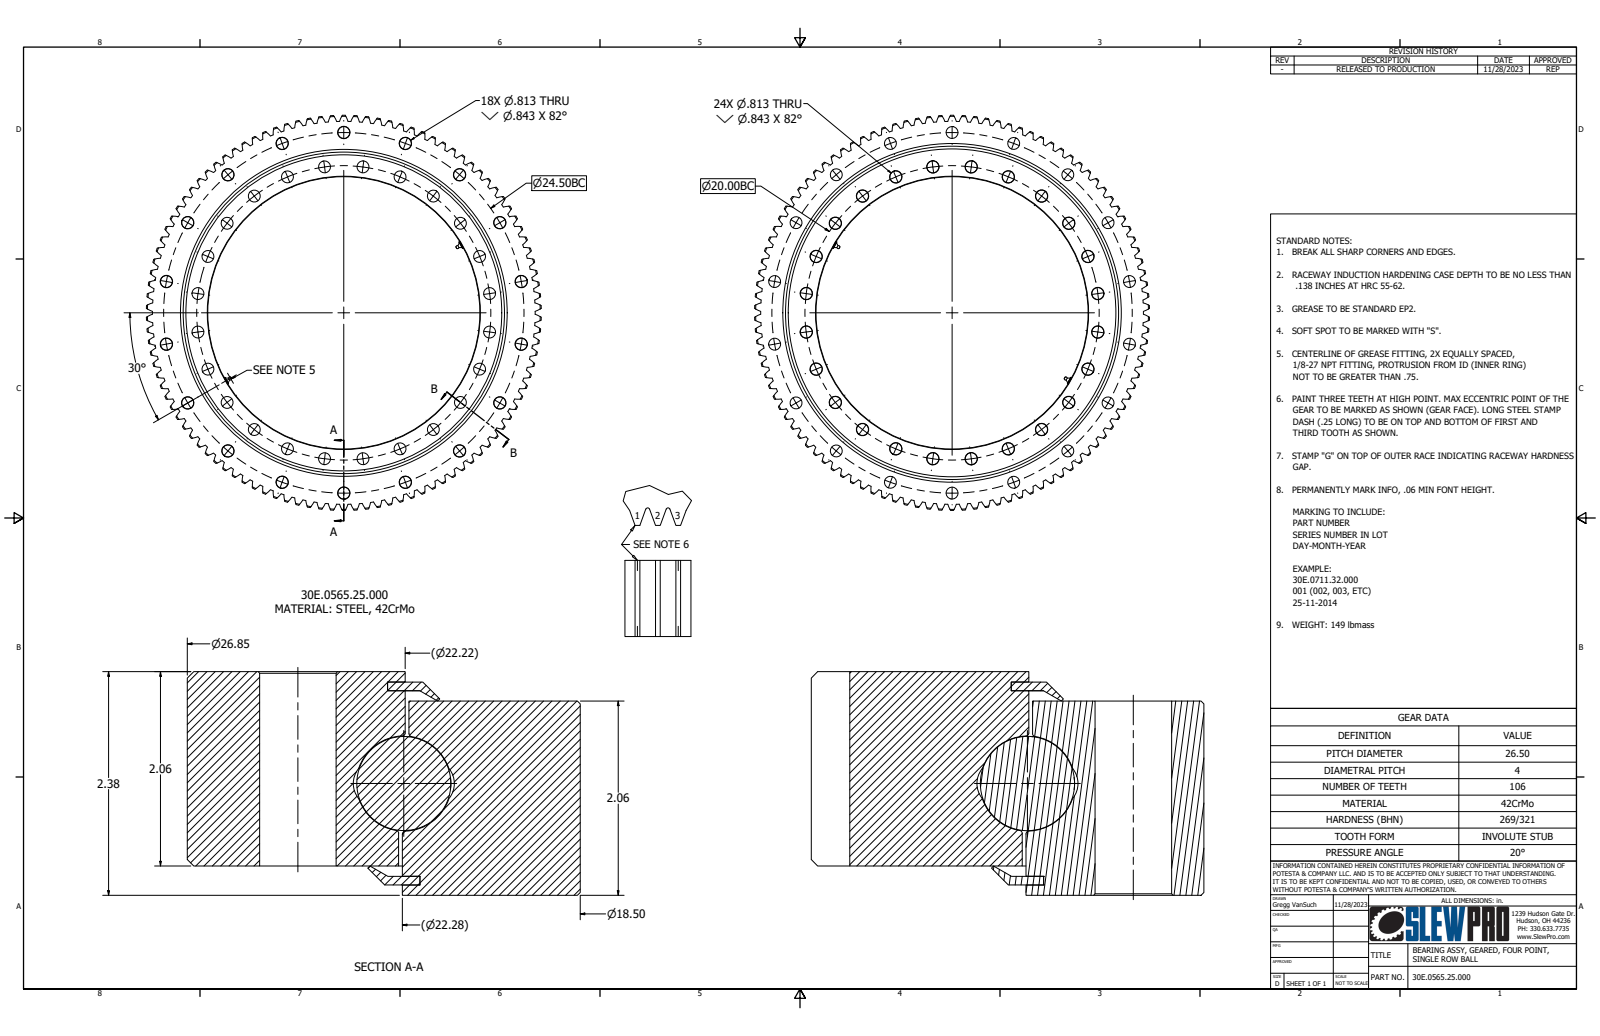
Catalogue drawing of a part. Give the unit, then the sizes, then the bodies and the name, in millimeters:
Units: millimetres
Overall size (bounding box): 682 × 681.8 × 60.3
Round holes (diameter × count): ⌀20.7 ×42, ⌀2.5 ×2, ⌀27.8 ×1, ⌀469.9 ×1, ⌀556.4 ×1, ⌀564.4 ×1, ⌀567.9 ×1, ⌀573.9 ×1
Round bosses / shafts (diameter × count): ⌀573.9 ×1, ⌀565.9 ×1, ⌀562.4 ×1, ⌀556.4 ×1, ⌀27.8 ×1
Partial cylindrical surfaces — rounded edges, fillets, slot ends (radius × count): R57.9 ×212, R330.5 ×1, R341 ×1
Main face-to-face distances: 52.4, 7.9, 60.3, 44.5, 2.8, 5.1, 2.8, 5.2, 2.4, 57.5
Hole centre spacings: 254, 503.7, 309.2, 359.2, 403, 439.9, 469.3, 490.7
Volume: 8 602 000 mm³ · Surface area: 1 257 000 mm²
Bodies: 8 solids, 932 faces (34 planar, 486 cylindrical, 412 other)
Part name (STEP PRODUCT): 30E.0565.25.000; Spur Gears1; 1_8 NPT Fitting
STEP written by: Autodesk Inventor 2026 (AUTOMOTIVE_DESIGN)
